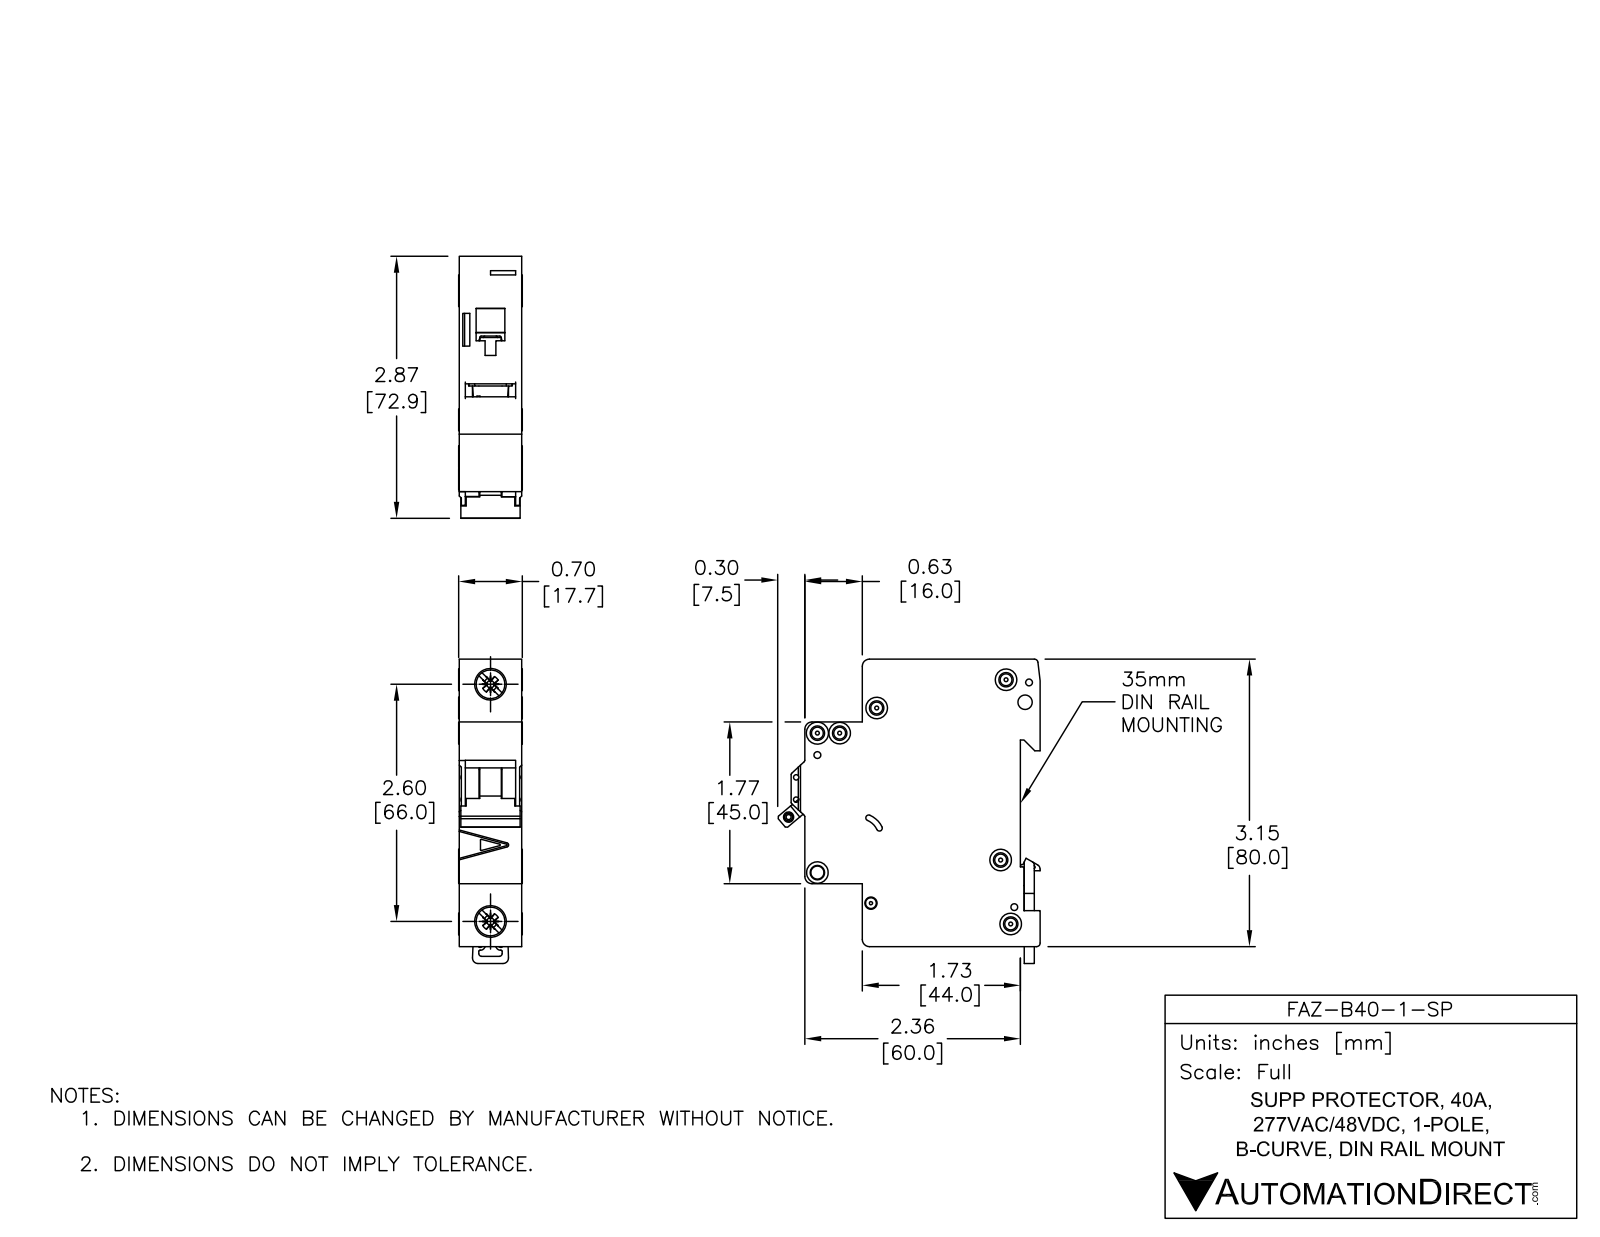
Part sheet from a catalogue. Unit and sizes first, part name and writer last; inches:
Units: inches
Overall size (bounding box): 3.338 × 2.876 × 0.697
Round holes (diameter × count): ⌀0.142 ×6, ⌀0.075 ×3, ⌀0.043 ×2, ⌀0.059 ×2, ⌀0.157 ×2, ⌀0.281 ×2, ⌀0.085 ×1, ⌀0.087 ×1, ⌀0.1 ×1, ⌀0.13 ×1, ⌀0.134 ×1
Round bosses / shafts (diameter × count): ⌀0.236 ×4, ⌀0.323 ×2, ⌀0.098 ×1
Partial cylindrical surfaces — rounded edges, fillets, slot ends (radius × count): R0.01 ×30, R0.02 ×13, R0.079 ×8, R0.008 ×5, R0.039 ×4, R0.031 ×2, R0.118 ×2, R0.059 ×1
Main face-to-face distances: 0.689, 3.129, 0.217, 1.949, 1.732, 2.579, 2.362, 0.63, 0.069, 0.62
Hole centre spacings: 0.244, 0.537, 0.189, 0.204, 0.221, 0.24, 0.254, 0.322
Volume: 4.573 in³ · Surface area: 30.29 in²
Bodies: 5 solids, 558 faces (235 planar, 202 cylindrical, 121 other)
Part name (STEP PRODUCT): FAZ-B40-1-SP
STEP written by: SolidWorks 2014 (AUTOMOTIVE_DESIGN)
